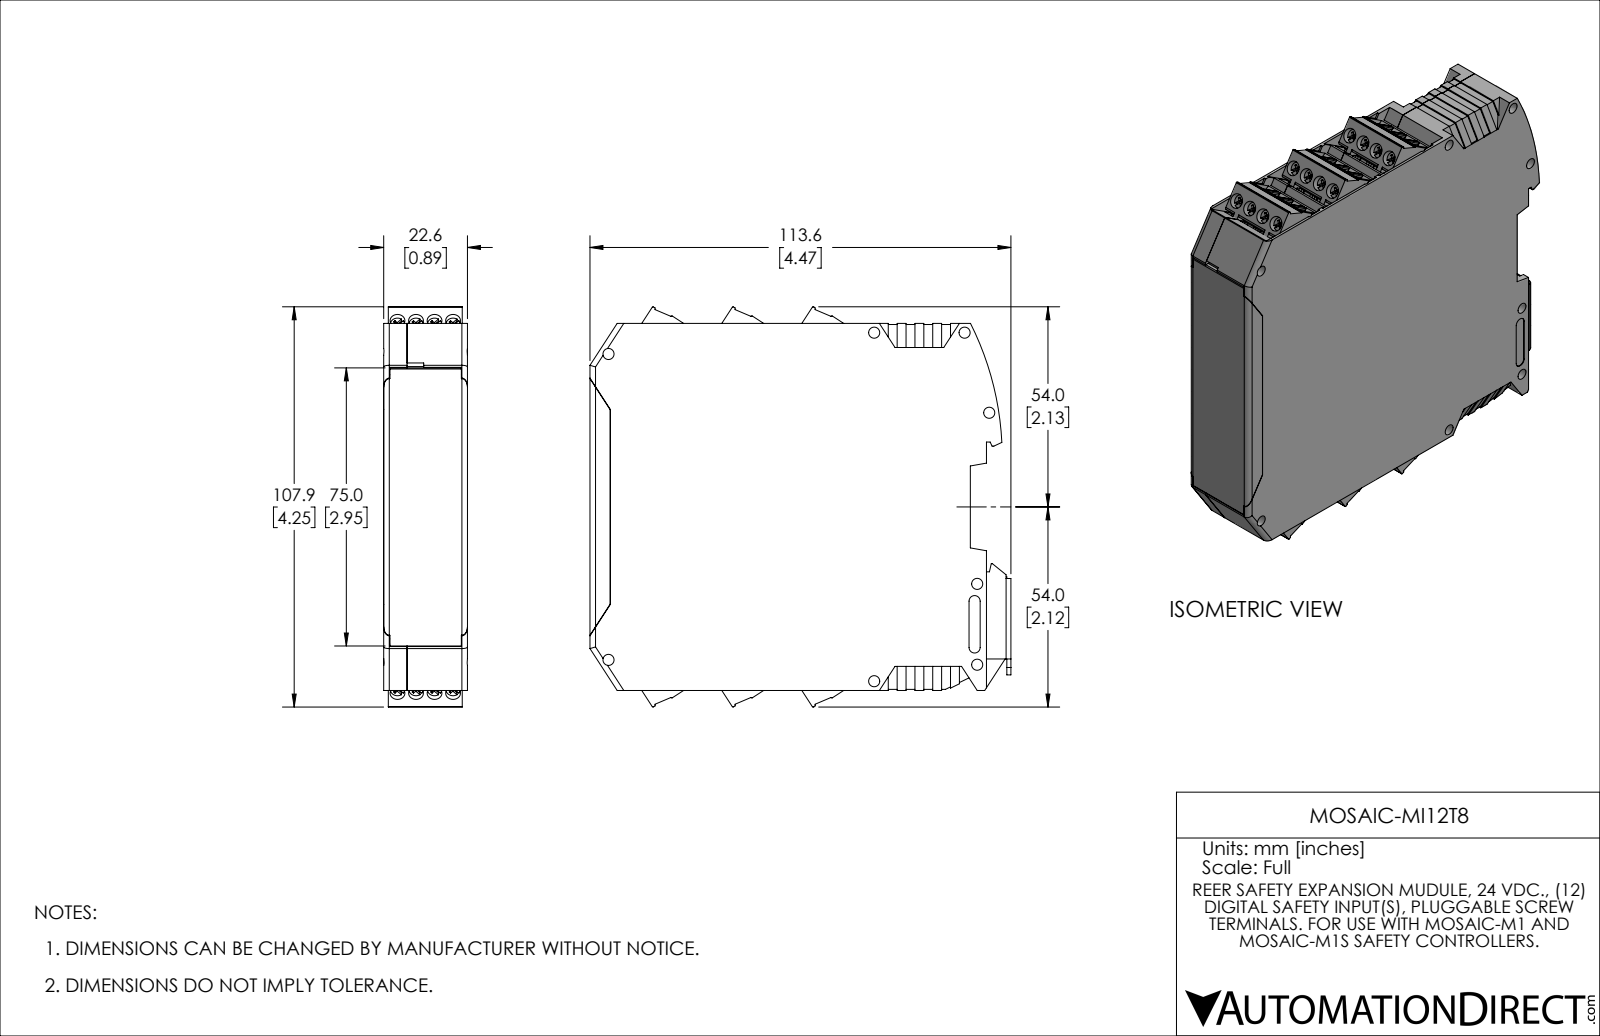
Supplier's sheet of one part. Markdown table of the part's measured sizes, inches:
| quantity | value |
| --- | --- |
| part name | MOSAIC-MI12T8 |
| STEP written by | SolidWorks 2021 (AUTOMOTIVE_DESIGN) |
| units | inches |
| bodies | 11 solids, 2255 faces (1901 planar, 351 cylindrical, 3 other) |
| overall size | 4.472 × 4.25 × 0.89 |
| volume | 3.801 in³ |
| surface area | 126.7 in² |
| round holes (diameter × count) | 0.055 × 26, 0.11 × 24, 0.157 × 24, 0.118 × 14, 0.063 × 1 |
| round bosses / shafts (diameter × count) | 0.149 × 24, 0.177 × 1, 0.11 × 1, 0.053 × 1 |
| partial cylindrical surfaces (radius × count) | 0.012 × 49, 0.114 × 24, 0.008 × 18, 0.03 × 18, 0.059 × 8, 0.024 × 6, 0.039 × 6, 0.098 × 5 |
| main face-to-face distances | 0.049, 0.841, 0.89, 0.791, 0.713, 0.197, 0.039, 0.811, 0.03, 0.248 |
| hole center spacings | 0.197, 0.394, 0.503, 0.74, 0.463, 0.591, 0.608, 0.713 |
